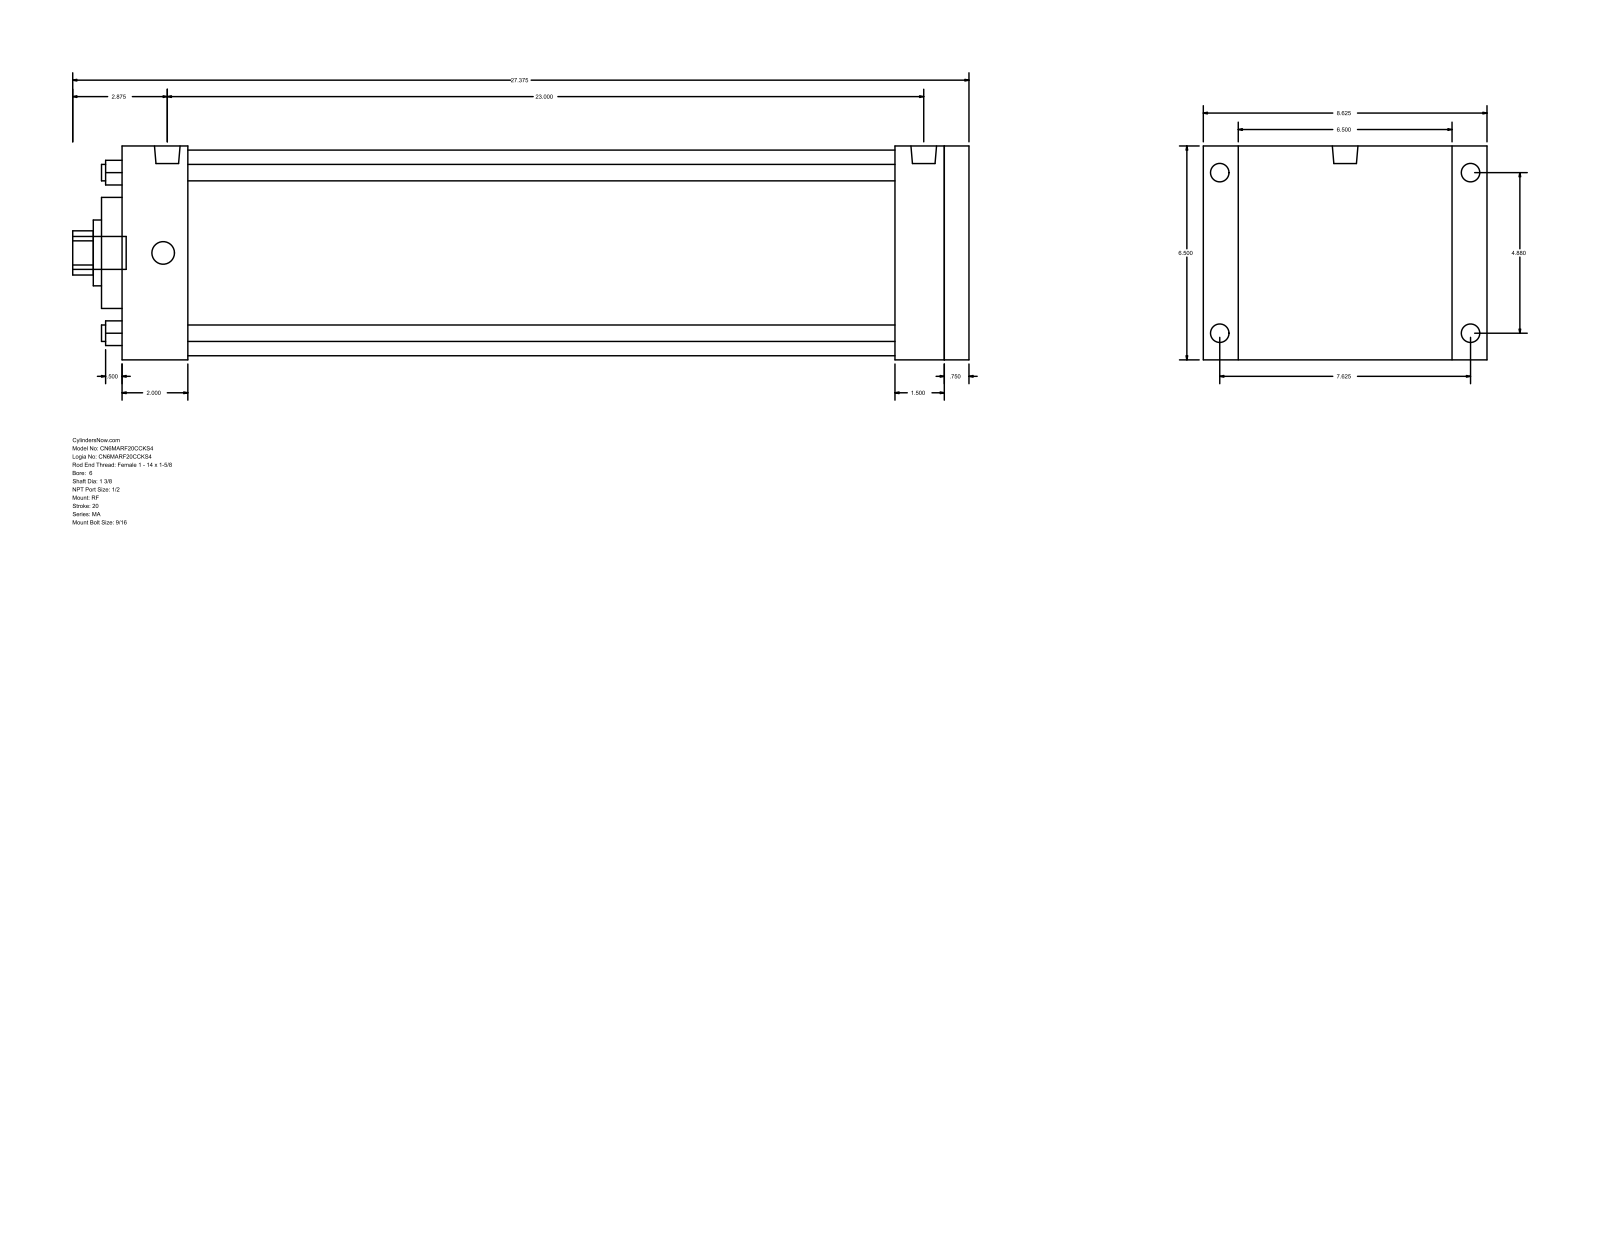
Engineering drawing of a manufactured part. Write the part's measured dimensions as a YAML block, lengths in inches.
part_name: "MA_RF__0600_1.375"
step_written_by: "GSSL Pune (CONFIG_CONTROL_DESIGN)"
units: inches
bodies: {solids: 0, faces: 94, planar: 65, cylindrical: 29, other: 0}
overall_size: [27.375, 8.625, 6.5]
round_holes:
  - {diameter: 0.5, count: 4}
  - {diameter: 1.375, count: 1}
  - {diameter: 2, count: 1}
  - {diameter: 3.375, count: 1}
  - {diameter: 6.25, count: 1}
round_bosses_or_shafts:
  - {diameter: 0.687, count: 4}
  - {diameter: 0.563, count: 4}
  - {diameter: 0.778, count: 2}
  - {diameter: 1, count: 1}
partial_cylinders:
  - {radius: 0.672, count: 1}
face_to_face_distances: [6.5, 25.875, 25.125, 0.75, 1.5, 2, 23.125, 23.875, 23.625, 21.625]
hole_center_spacings: [3.451, 4.88, 6.902]
